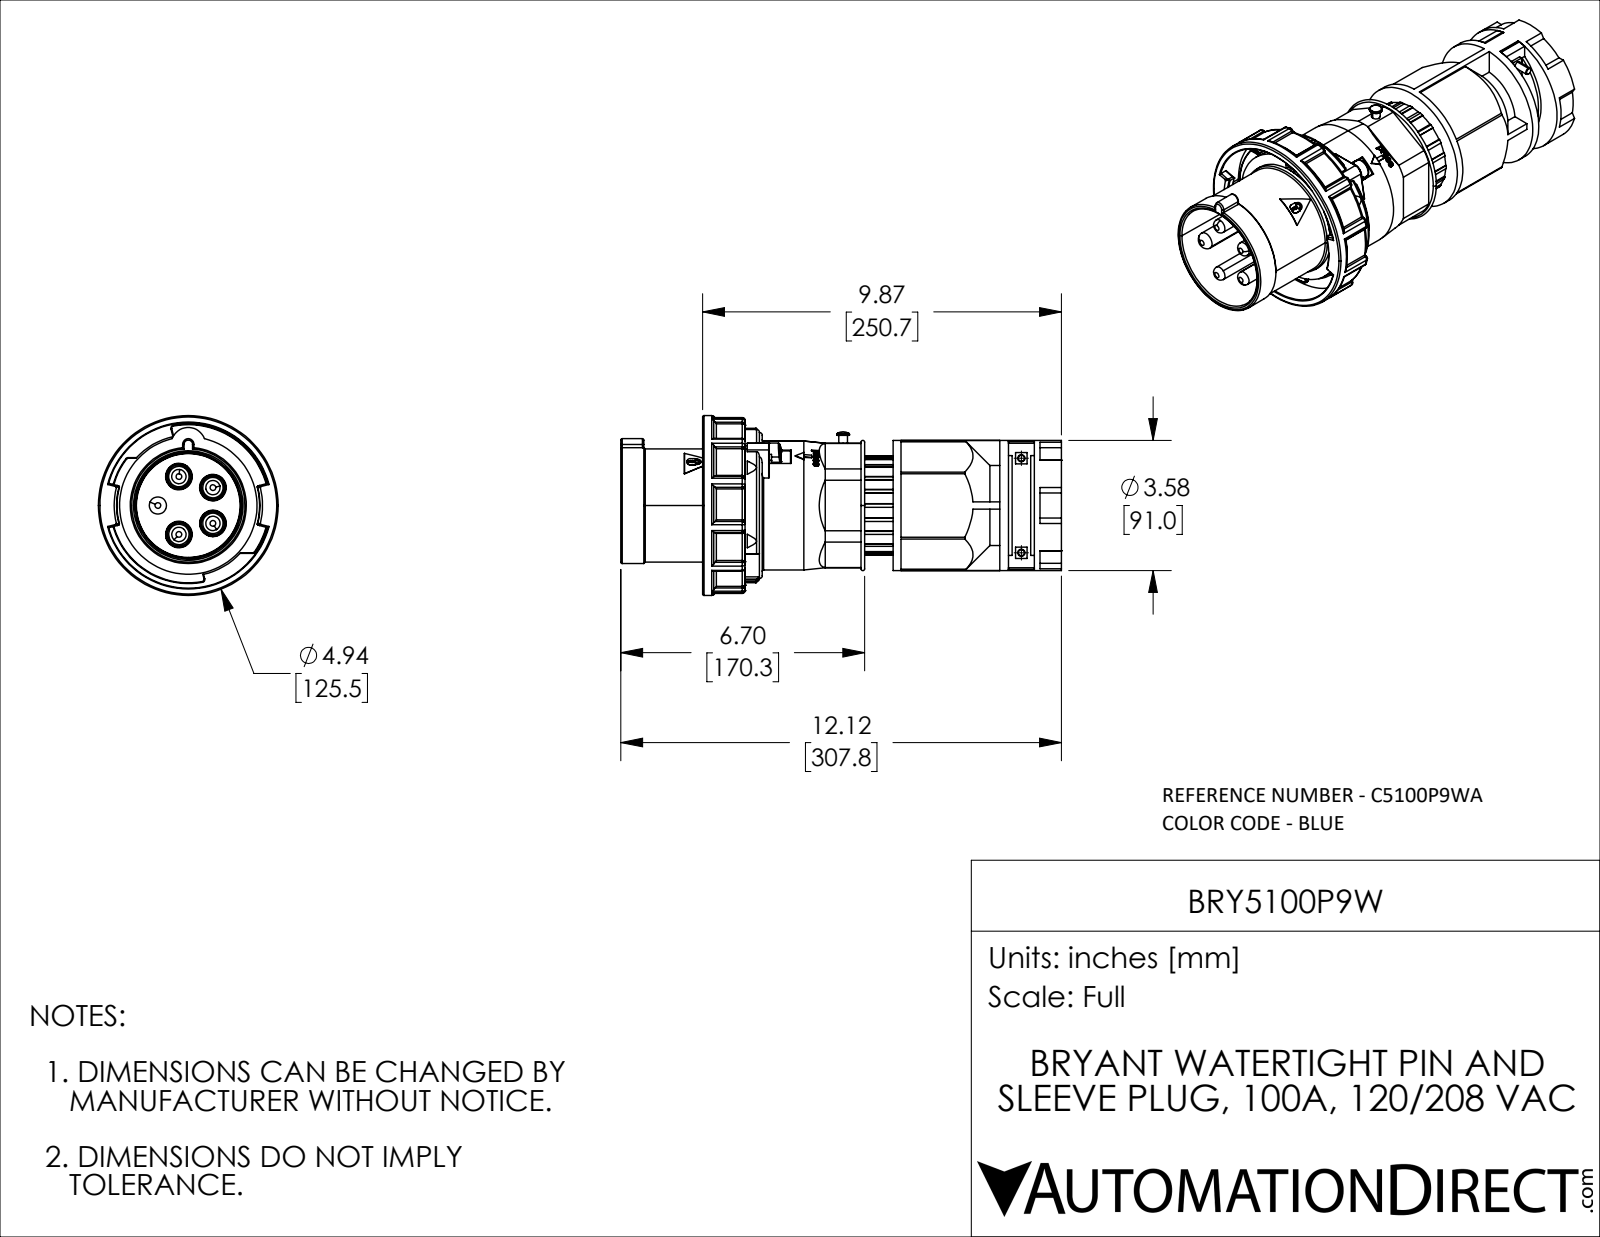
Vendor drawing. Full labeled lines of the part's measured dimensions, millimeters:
Part name (STEP PRODUCT): BRY5100P9W
STEP written by: SolidWorks 2021 (CONFIG_CONTROL_DESIGN)
Units: millimetres
Bodies: 6 solids, 1303 faces (389 planar, 442 cylindrical, 472 other)
Overall size (bounding box): 307.75 × 125.5 × 125.5
Volume: 1 157 000 mm³ · Surface area: 217 393 mm²
Round holes (diameter × count): ⌀50 ×1, ⌀81 ×1, ⌀115.5 ×1
Round bosses / shafts (diameter × count): ⌀10 ×4, ⌀5 ×2, ⌀125.5 ×1, ⌀116.87 ×1, ⌀96 ×1, ⌀91 ×1, ⌀90 ×1, ⌀81.1 ×1
Partial cylindrical surfaces — rounded edges, fillets, slot ends (radius × count): R2 ×52, R1 ×42, R0.5 ×18, R2.5 ×6, R1.2 ×2, R1.75 ×2, R4 ×2, R6 ×2
Main face-to-face distances: 79.5, 118.5, 18, 100.5, 2.5, 24, 27, 32.67, 46.83, 94.5
